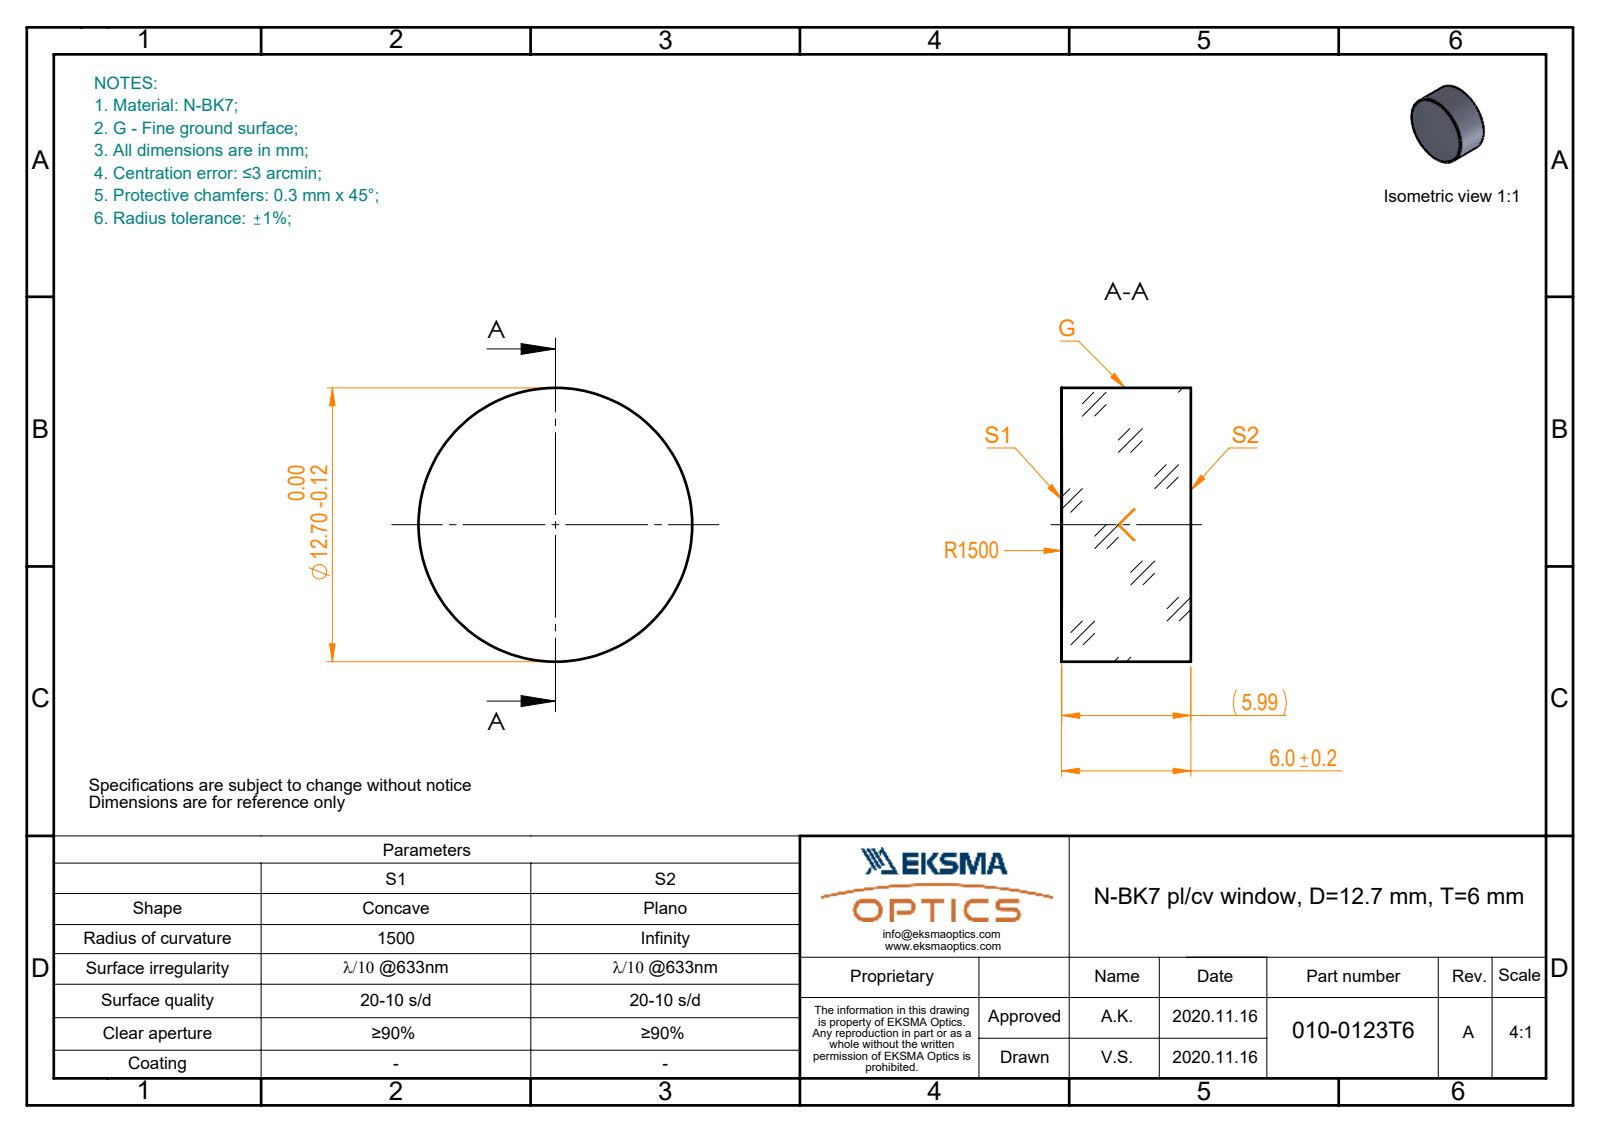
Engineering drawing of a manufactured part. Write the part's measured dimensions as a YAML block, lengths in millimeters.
part_name: "010-0123T6_N-BK7_PCV_window"
step_written_by: "SolidWorks 2019 (CONFIG_CONTROL_DESIGN)"
units: millimeters
bodies: {solids: 1, faces: 5, planar: 1, cylindrical: 2, other: 2}
overall_size: [12.7, 12.7, 6]
volume: 759
surface_area: 493
round_bosses_or_shafts:
  - {diameter: 12.7, count: 1}
